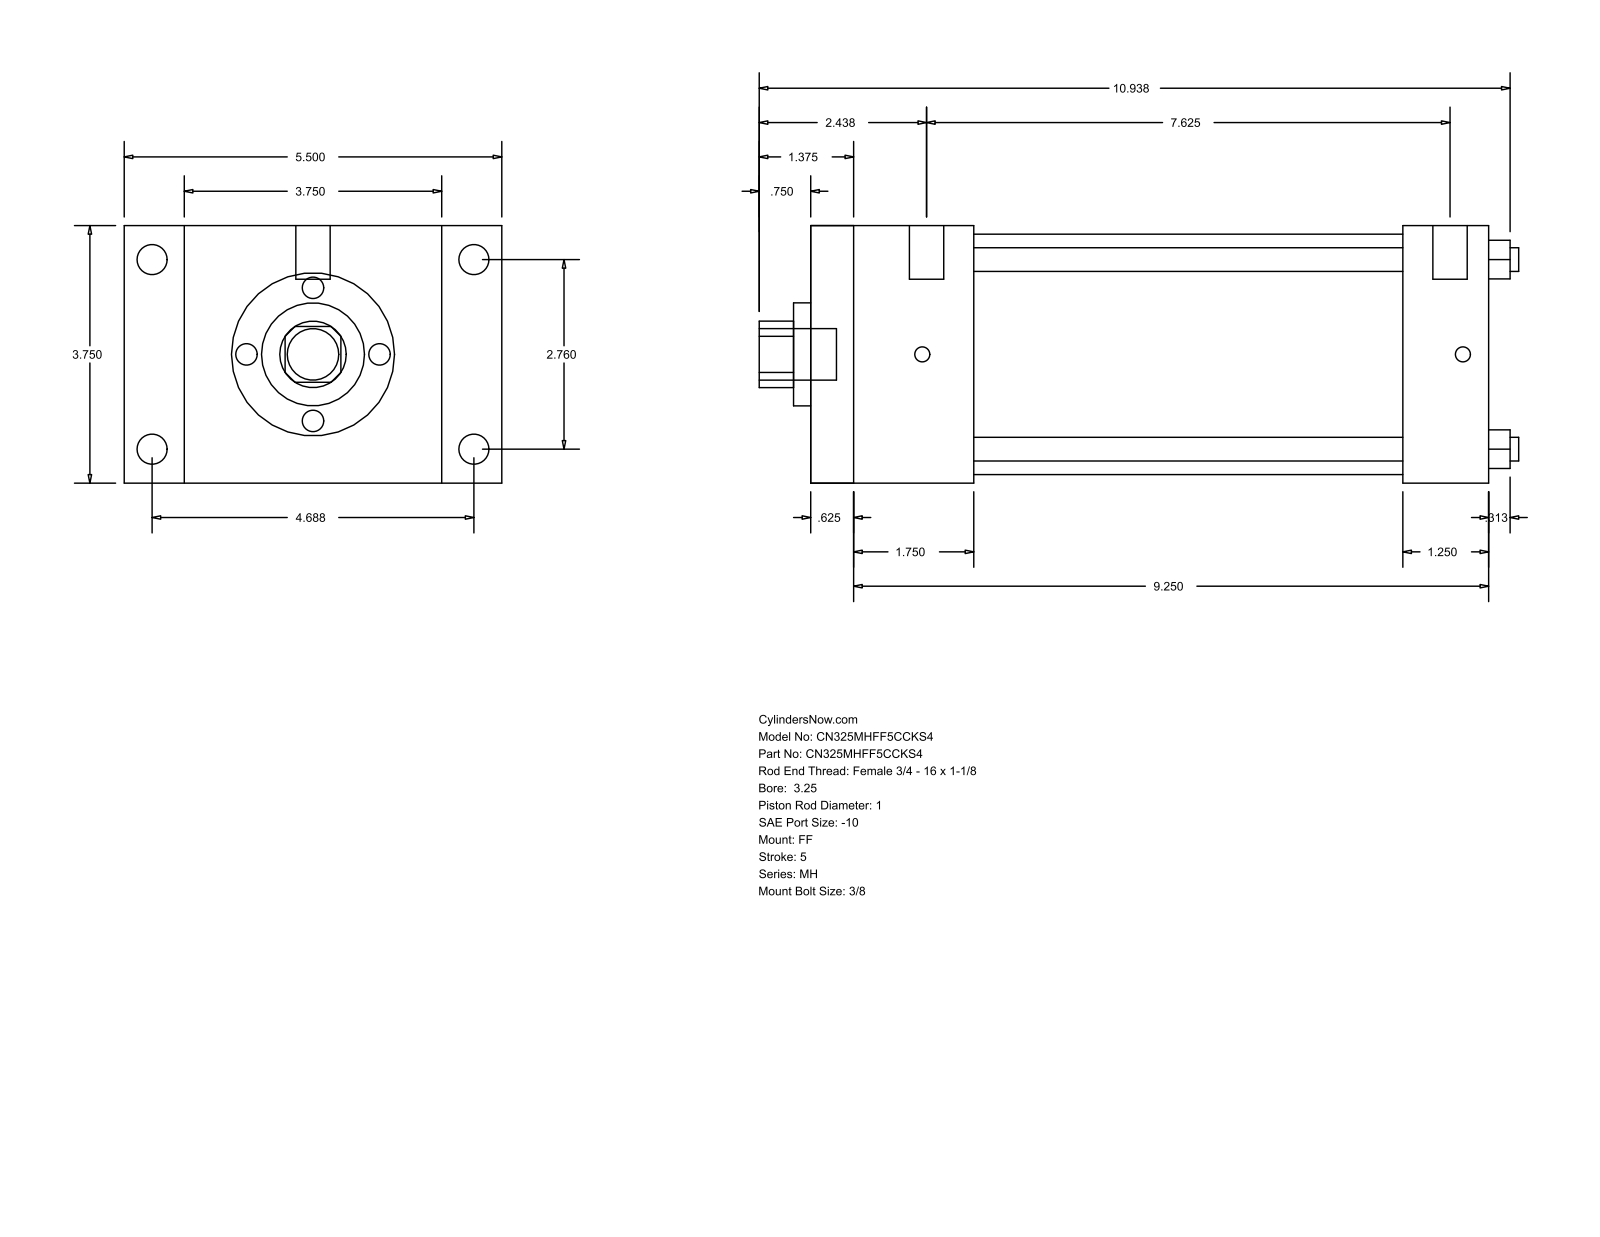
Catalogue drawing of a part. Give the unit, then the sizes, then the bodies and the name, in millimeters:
Units: millimetres
Overall size (bounding box): 280.99 × 139.7 × 95.25
Round holes (diameter × count): ⌀8.76 ×4, ⌀25.4 ×1, ⌀38.1 ×1, ⌀88.9 ×1
Round bosses / shafts (diameter × count): ⌀11.13 ×4, ⌀5.56 ×4, ⌀12.7 ×2, ⌀19.05 ×1
Partial cylindrical surfaces — rounded edges, fillets, slot ends (radius × count): R12.29 ×1
Main face-to-face distances: 95.24, 250.83, 15.87, 234.96, 22.23, 117.47, 219.07, 203.2, 31.76, 60.33
Hole centre spacings: 49.57, 70.1, 99.14
Bodies: 0 solids, 92 faces (64 planar, 28 cylindrical, 0 other)
Part name (STEP PRODUCT): MH_FF__0325_1
STEP written by: GSSL Pune (CONFIG_CONTROL_DESIGN)
